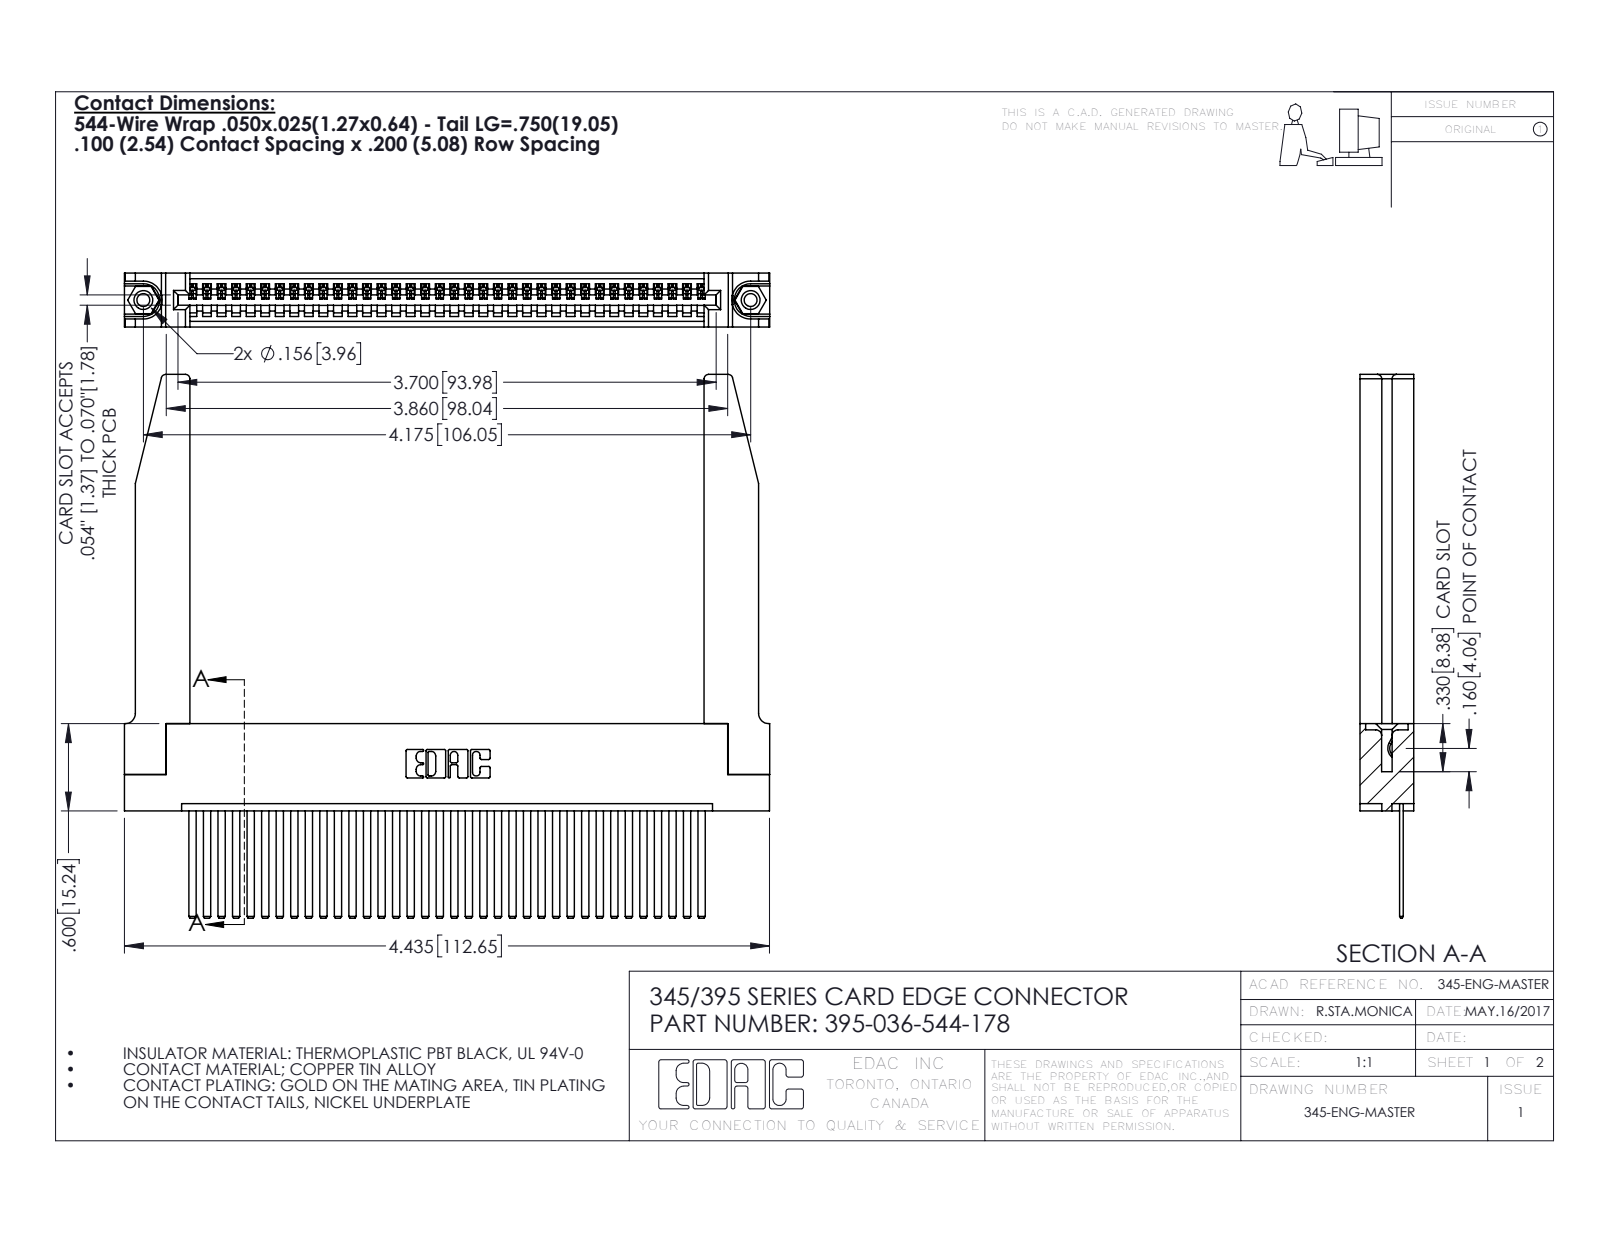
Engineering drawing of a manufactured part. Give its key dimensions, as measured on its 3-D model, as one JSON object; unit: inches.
{"part_name": "345-292-001_345-293-144; 395-036-544-178; 345 Part_Flush Mounting Lugs - 0.156 Dia-TH; 345-220-078_345-220-078 (+1 more)", "step_written_by": "SolidWorks 2016 (CONFIG_CONTROL_DESIGN)", "units": "inches", "bodies": {"solids": 41, "faces": 2232, "planar": 1518, "cylindrical": 662, "other": 52}, "overall_size": [4.436, 3.737, 0.37], "volume_in3": 1.15, "surface_area_in2": 35.23, "round_holes": [[0.089, 2], [0.125, 2], [0.156, 2], [0.064, 1]], "round_bosses_or_shafts": [[0.155, 2]], "partial_cylinders_radius": [[0.006, 72], [0.01, 22], [0.03, 8], [0.007, 6], [0.031, 6], [0.026, 3], [0.031, 2], [0.04, 2]], "face_to_face_distances": [0.072, 0.298, 0.37, 0.098, 0.272, 0.025, 0.2, 0.225, 0.148, 0.15], "hole_center_spacings": [0.27, 3.939, 4.175]}
